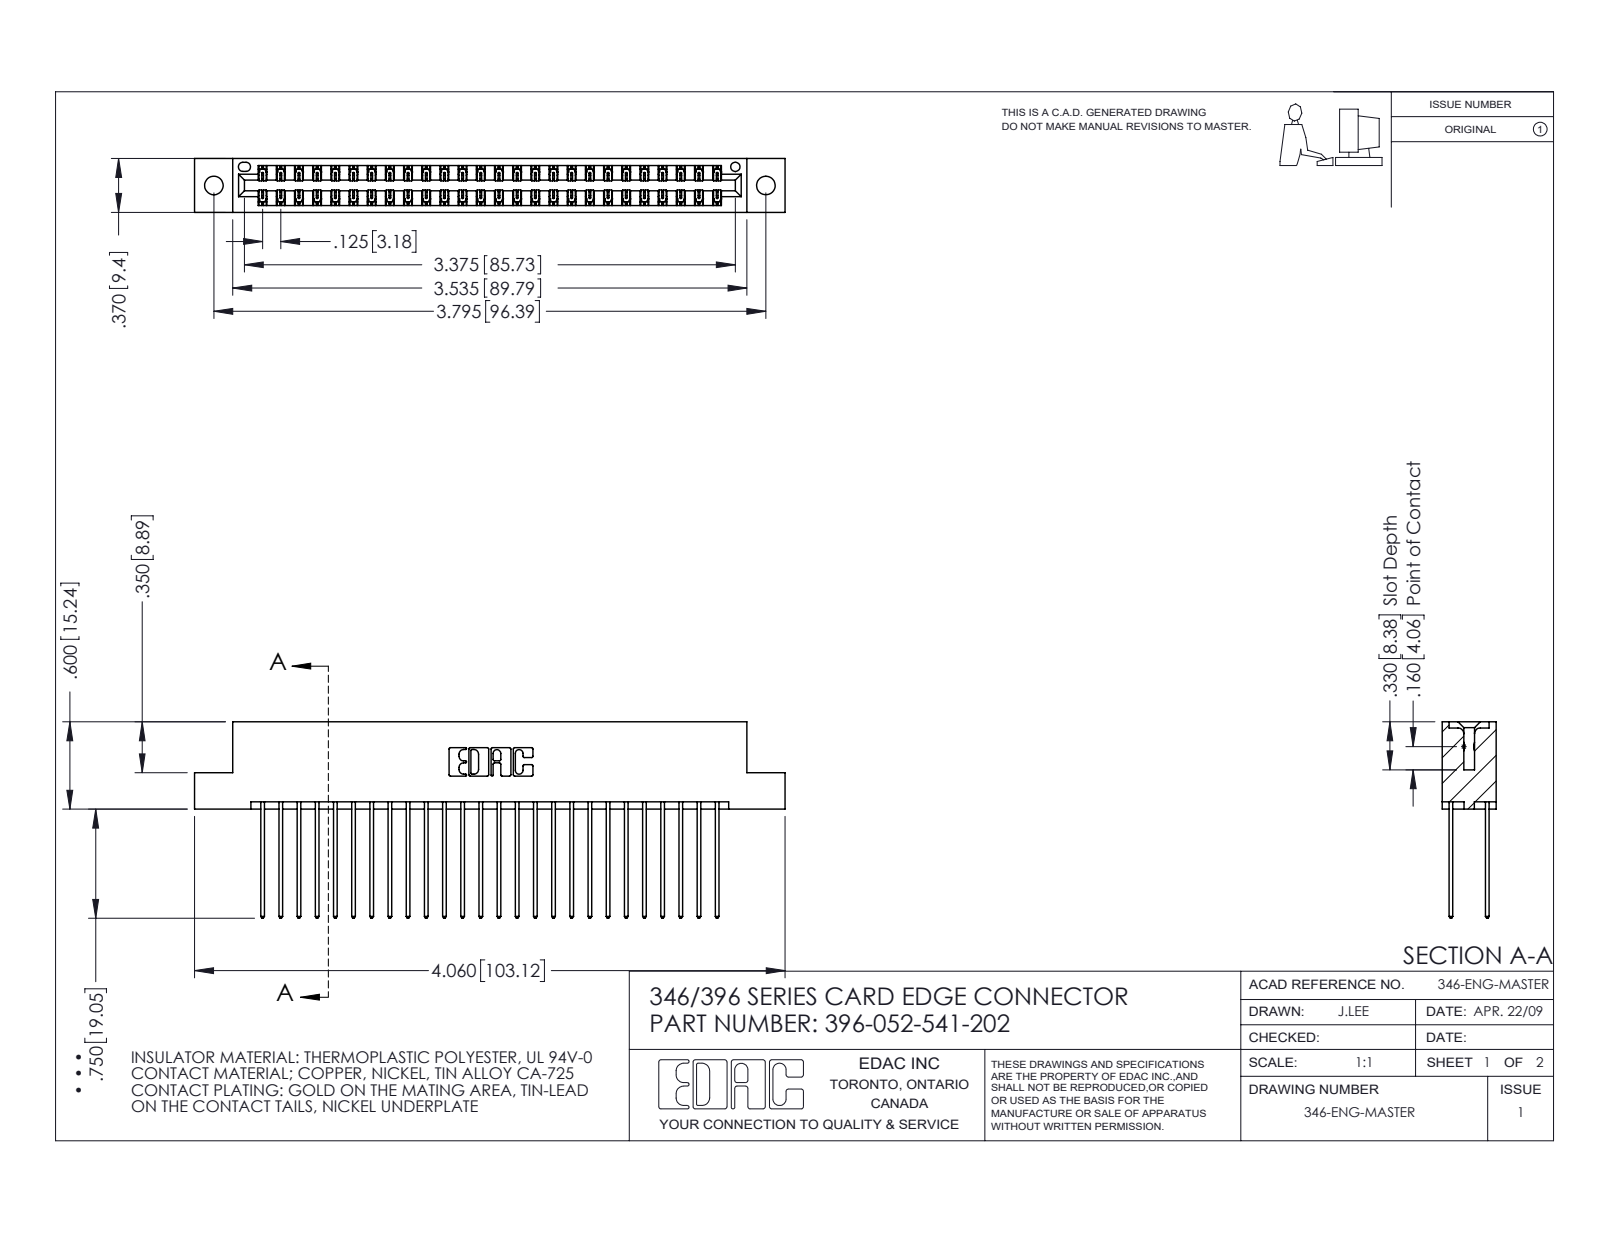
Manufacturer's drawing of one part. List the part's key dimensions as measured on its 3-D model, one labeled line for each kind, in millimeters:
Part name (STEP PRODUCT): 396-052-541-202; 345-292-001_345-293-141; 346 Part_Flush Mounting Lugs - 0.128 Dia
STEP written by: SolidWorks 2016 (CONFIG_CONTROL_DESIGN)
Units: millimetres
Bodies: 53 solids, 2826 faces (1896 planar, 930 cylindrical, 0 other)
Overall size (bounding box): 103.1 × 34.3 × 9.4
Volume: 10 200 mm³ · Surface area: 14 920 mm²
Round holes (diameter × count): ⌀3.3 ×2, ⌀1.6 ×1
Partial cylindrical surfaces — rounded edges, fillets, slot ends (radius × count): R0.2 ×78, R0.3 ×52, R0.3 ×22, R0.2 ×6, R0.8 ×6, R0.7 ×3, R0.4 ×2, R0.6 ×2
Main face-to-face distances: 1.2, 8.2, 6.4, 1.8, 7.6, 0.6, 9.4, 7, 5.7, 3.8
Hole centre spacings: 6.2, 91.1, 96.4
